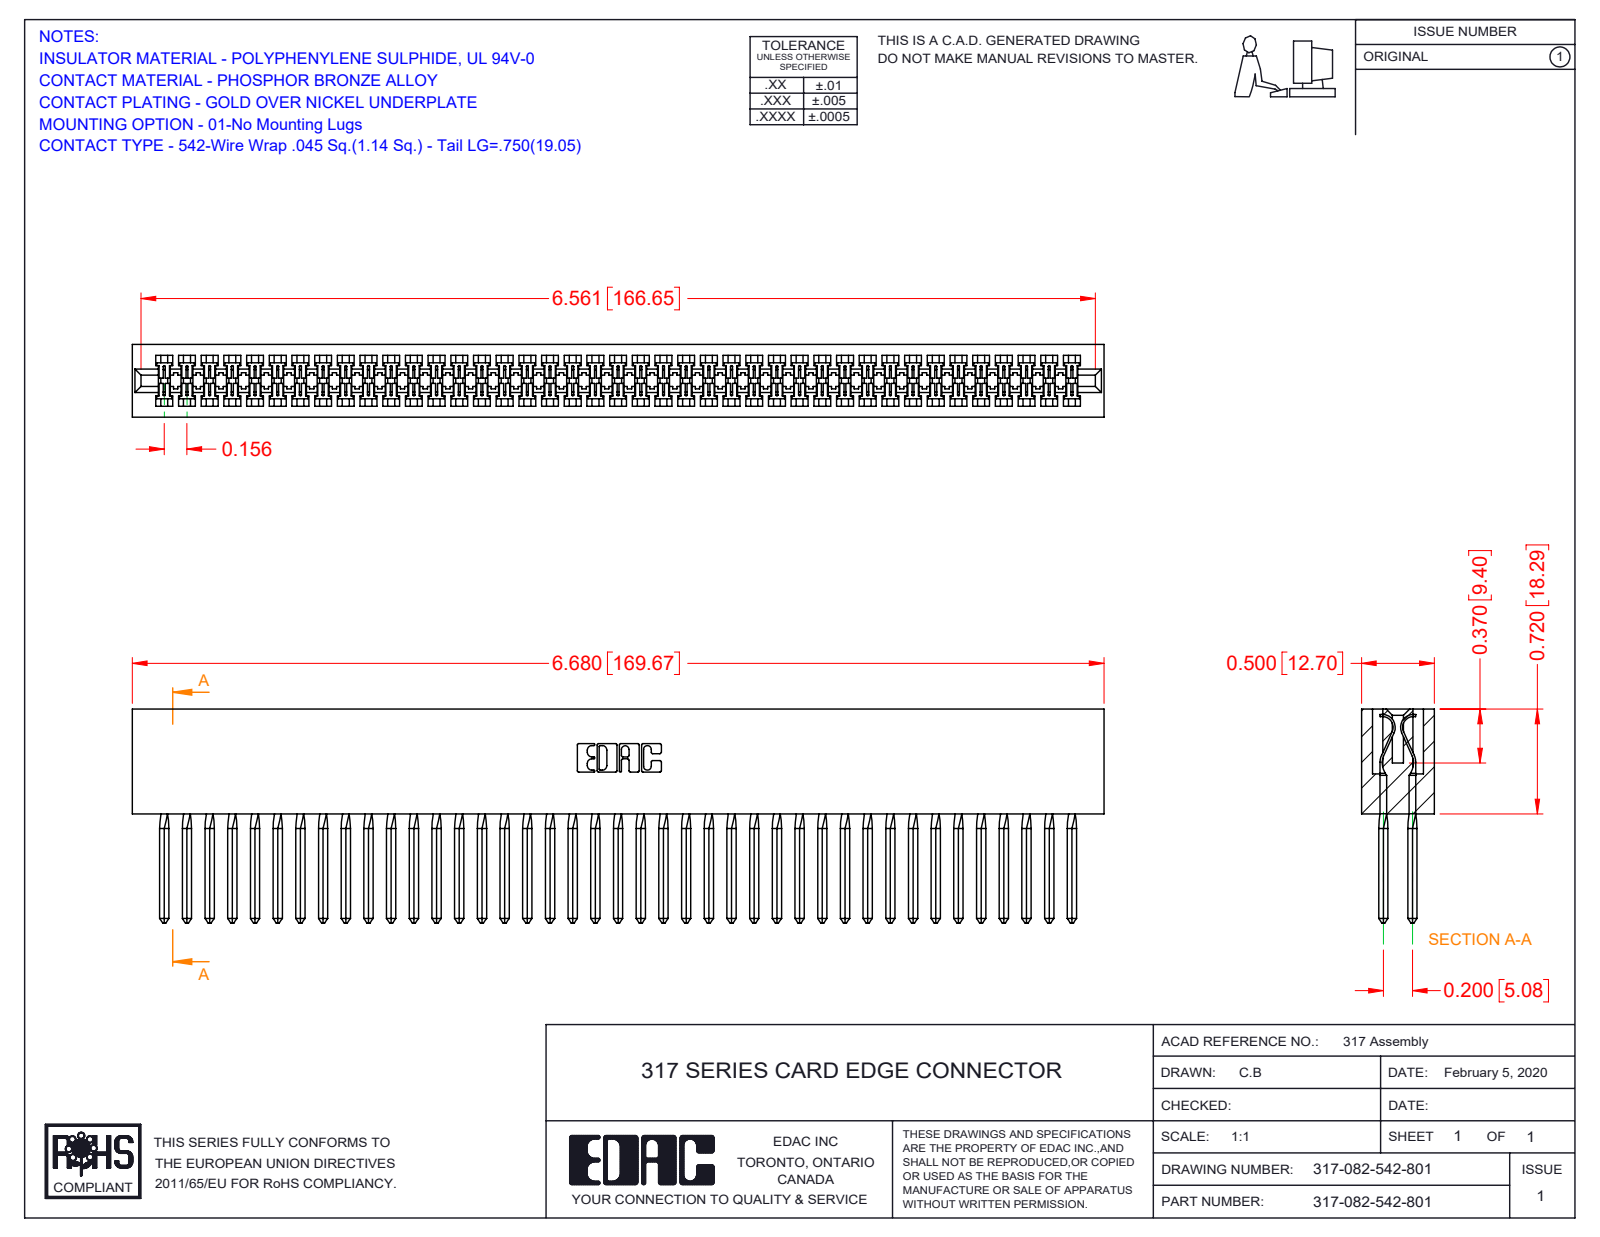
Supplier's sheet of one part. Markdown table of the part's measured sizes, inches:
| quantity | value |
| --- | --- |
| part name | 317-290-003_542; 317-082-542-801; 317 Part_Lugless |
| STEP written by | SolidWorks 2016 (CONFIG_CONTROL_DESIGN) |
| units | inches |
| bodies | 83 solids, 4764 faces (3822 planar, 614 cylindrical, 328 other) |
| overall size | 6.68 × 1.47 × 0.5 |
| volume | 1.799 in³ |
| surface area | 63.77 in² |
| partial cylindrical surfaces (radius × count) | 0.006 × 164, 0.01 × 22, 0.007 × 6, 0.031 × 6, 0.026 × 3, 0.074 × 2, 0.089 × 2, 0.1 × 2 |
| main face-to-face distances | 0.075, 0.5, 0.425, 0.35, 0.2, 0.046, 0.128, 0.372, 0.052, 0.297 |
